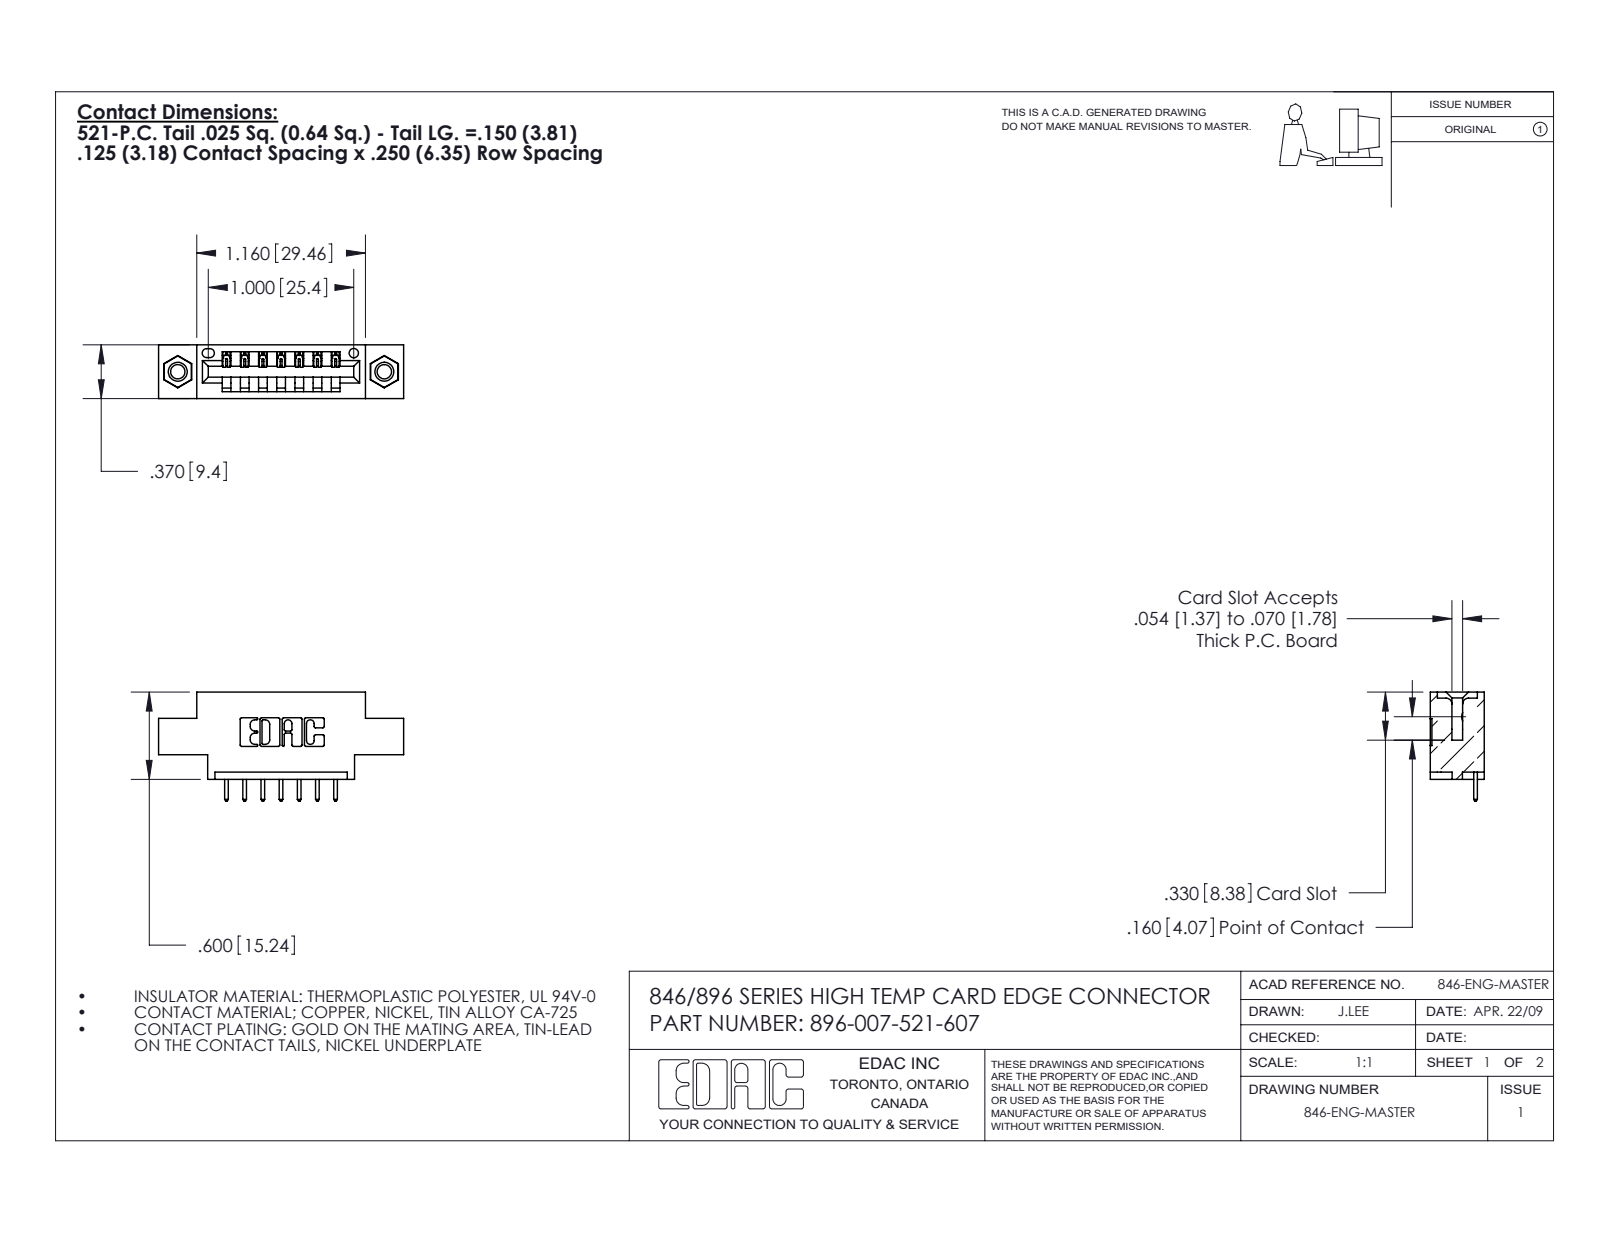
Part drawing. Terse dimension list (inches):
name: 345-292-001_345-293-121; 346 Part_0.170 Offset - 0.156 Dia-TI; 345-250-001_345-250-005-103; 396-007-521-607
written by: SolidWorks 2016 (CONFIG_CONTROL_DESIGN)
unit: in
bodies: 10 solids, 592 faces (392 planar, 184 cylindrical, 16 other)
size: 1.685 × 0.75 × 0.37
volume: 0.224 in³; area: 6.699 in²
holes: 2× ⌀0.098, 2× ⌀0.125, 2× ⌀0.156, 1× ⌀0.064
bosses: 2× ⌀0.155
rounds: 22× R0.01, 14× R0.006, 14× R0.01, 6× R0.007, 6× R0.031, 3× R0.026, 2× R0.031, 2× R0.04
face distances: 0.25, 0.37, 0.048, 0.322, 0.222, 0.148, 0.1, 0.174, 0.125, 0.185
hole spacings: 0.246, 1.217, 1.42
